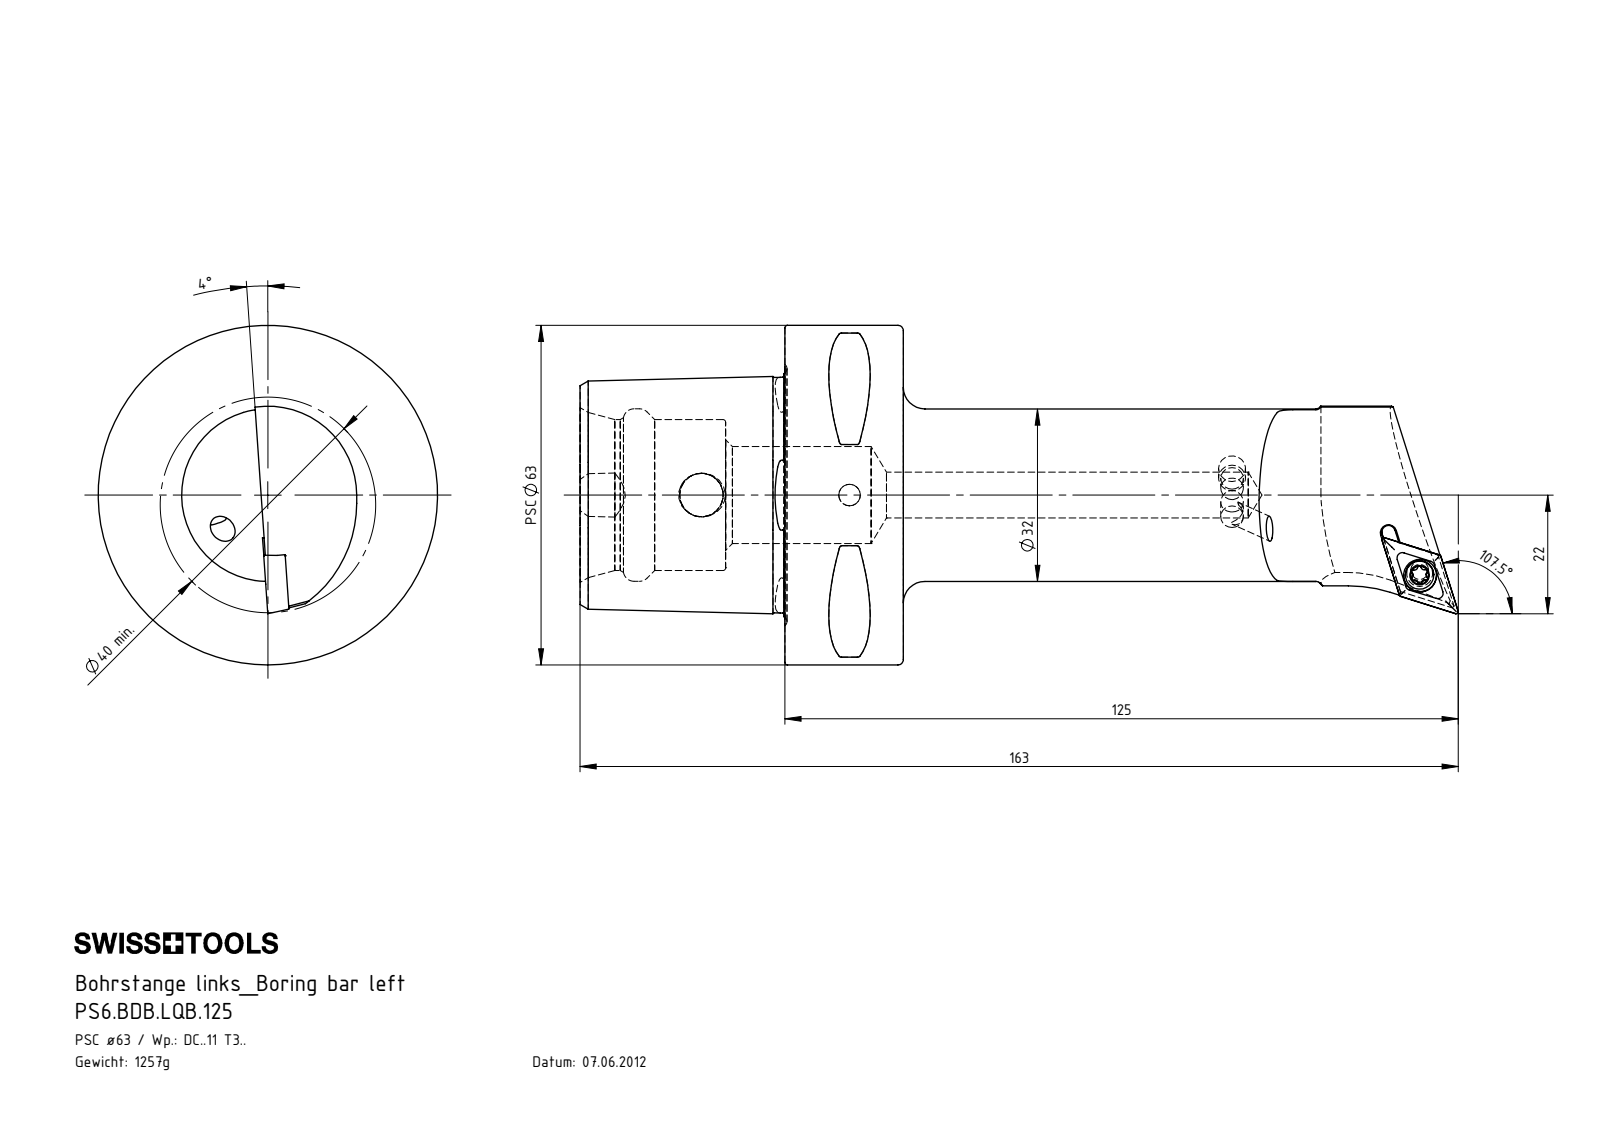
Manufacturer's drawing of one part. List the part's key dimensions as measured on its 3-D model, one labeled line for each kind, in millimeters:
Part name (STEP PRODUCT): KVT_MB_600_050; DCMT11T304; WCB-ER2.001.009_A; PS6-BDB.LQB.125_A (+1 more)
STEP written by: SolidWorks 2017 (AUTOMOTIVE_DESIGN)
Units: millimetres
Bodies: 5 solids, 289 faces (53 planar, 75 cylindrical, 161 other)
Overall size (bounding box): 163 × 63 × 63
Volume: 160 914 mm³ · Surface area: 32 180 mm²
Round holes (diameter × count): ⌀4 ×2, ⌀4.2 ×2, ⌀3.3 ×1, ⌀4.4 ×1, ⌀6.1 ×1, ⌀8.1 ×1, ⌀8.5 ×1, ⌀18 ×1, ⌀28 ×1, ⌀32 ×1
Round bosses / shafts (diameter × count): ⌀63 ×1, ⌀5.25 ×1, ⌀5 ×1, ⌀4 ×1
Partial cylindrical surfaces — rounded edges, fillets, slot ends (radius × count): R0.5 ×8, R0.34 ×6, R0.59 ×6, R1.25 ×1, R3 ×1, R6 ×1, R16.5 ×1, R23 ×1
Main face-to-face distances: 22, 38, 60, 24.88, 27, 11, 33, 55.8, 3.67, 37.8
Hole centre spacings: 27.5
